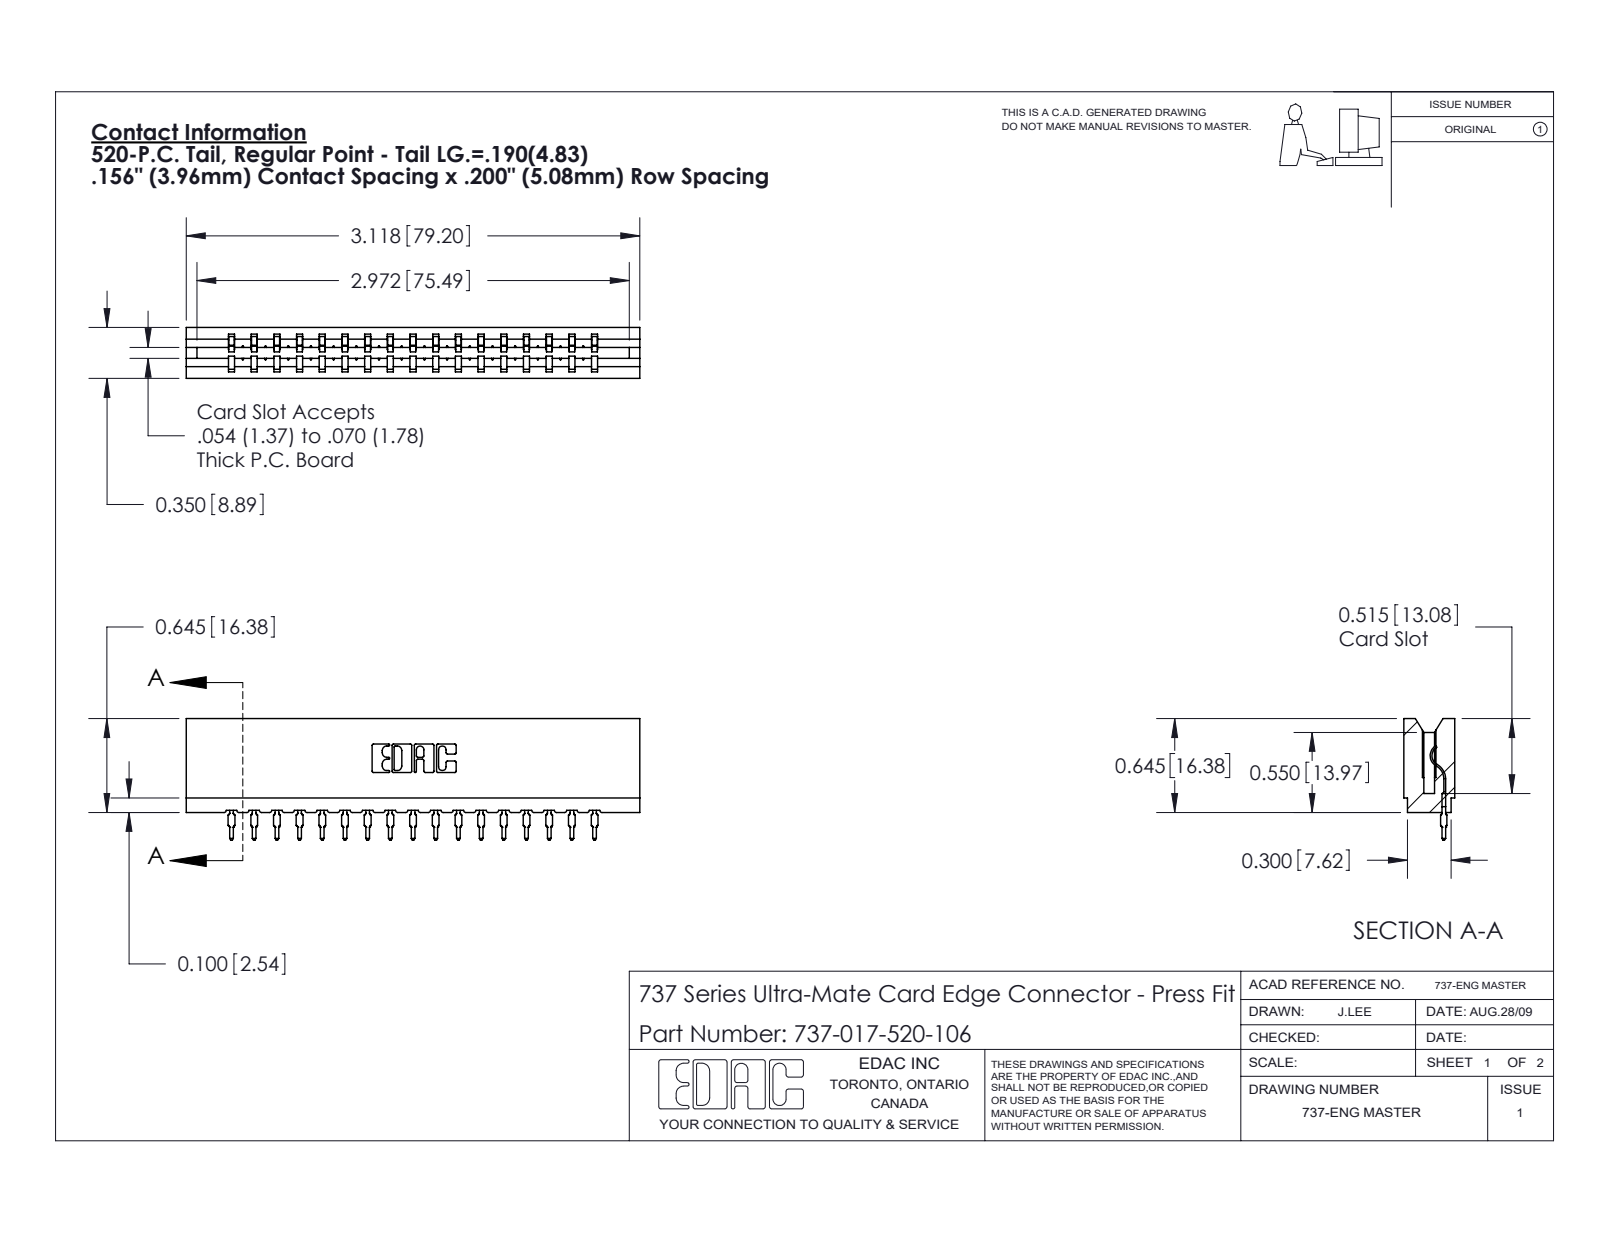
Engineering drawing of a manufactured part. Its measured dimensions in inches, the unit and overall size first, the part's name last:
Units: inches
Overall size (bounding box): 3.118 × 0.836 × 0.35
Partial cylindrical surfaces — rounded edges, fillets, slot ends (radius × count): R0.015 ×34, R0.021 ×34, R0.01 ×22, R0.007 ×6, R0.031 ×6, R0.005 ×4, R0.011 ×4, R0.026 ×3
Main face-to-face distances: 0.138, 0.212, 0.35, 0.156, 0.624, 0.78, 0.312, 0.468, 0.074, 0.936
Volume: 0.475 in³ · Surface area: 15.33 in²
Bodies: 18 solids, 2016 faces (1211 planar, 363 cylindrical, 442 other)
Part name (STEP PRODUCT): 737-017-520-106; 737 Part_Insulator Option - 06; 745-292-001_520
STEP written by: SolidWorks 2020 (CONFIG_CONTROL_DESIGN)
